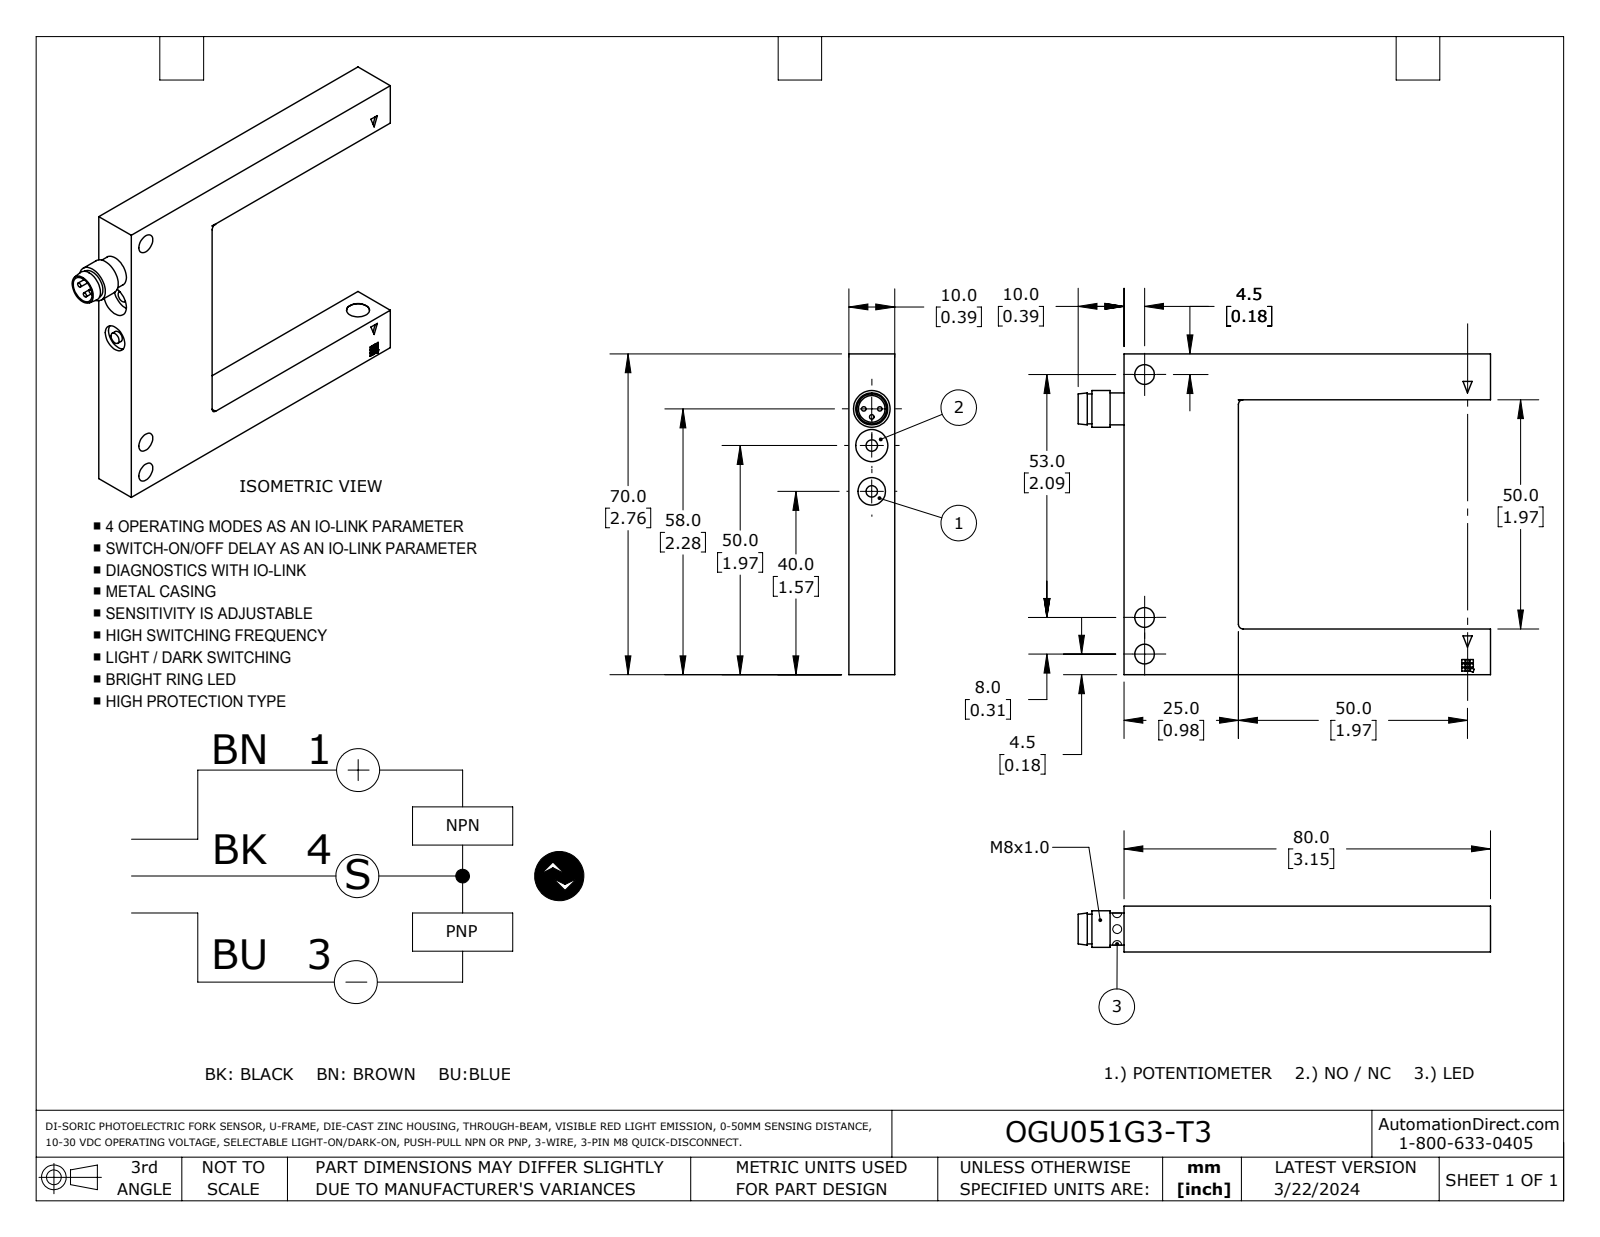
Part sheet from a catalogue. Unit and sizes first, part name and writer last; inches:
Units: inches
Overall size (bounding box): 3.543 × 2.756 × 0.394
Round holes (diameter × count): ⌀0.169 ×3, ⌀0.118 ×1, ⌀0.197 ×1, ⌀0.228 ×1, ⌀0.236 ×1, ⌀0.276 ×1
Round bosses / shafts (diameter × count): ⌀0.039 ×3, ⌀0.098 ×2, ⌀0.315 ×1, ⌀0.276 ×1, ⌀0.256 ×1
Partial cylindrical surfaces — rounded edges, fillets, slot ends (radius × count): R0.039 ×3
Main face-to-face distances: 0.394, 2.362, 2.756, 1.969, 0.984, 3.15, 2.165, 0.392, 0.039, 2.364
Hole centre spacings: 0.315, 0.394, 0.709, 2.087, 2.402
Volume: 1.722 in³ · Surface area: 16.5 in²
Bodies: 1 solid, 112 faces (91 planar, 20 cylindrical, 1 other)
Part name (STEP PRODUCT): OGU051G3-T3
STEP written by: SolidWorks 2023 (AUTOMOTIVE_DESIGN)
